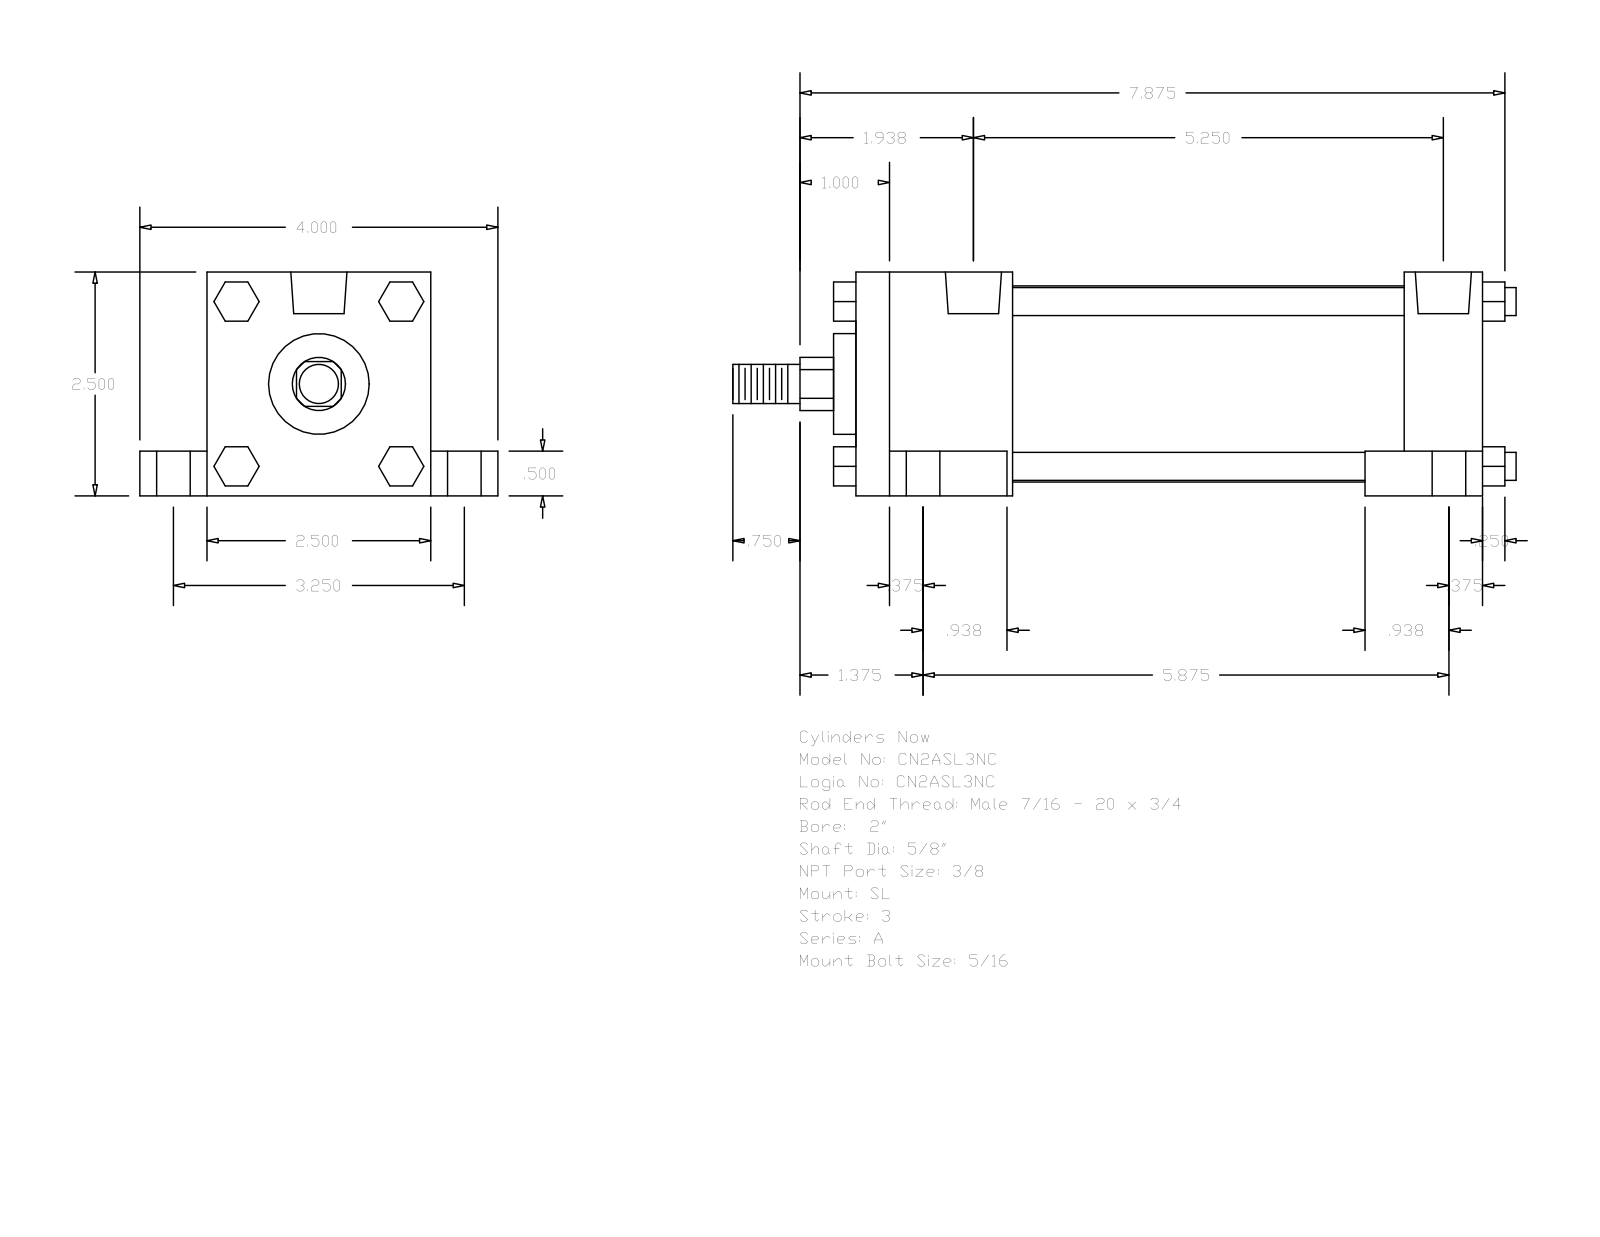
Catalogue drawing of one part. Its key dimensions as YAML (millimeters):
part_name: "A_SL__0200_0.625"
step_written_by: "GSSL Pune (CONFIG_CONTROL_DESIGN)"
units: millimeters
bodies: {solids: 0, faces: 148, planar: 112, cylindrical: 36, other: 0}
overall_size: [222.25, 101.6, 63.5]
round_holes:
  - {diameter: 5.56, count: 4}
  - {diameter: 9.53, count: 4}
  - {diameter: 15.88, count: 4}
  - {diameter: 15.93, count: 2}
round_bosses_or_shafts:
  - {diameter: 7.94, count: 4}
  - {diameter: 55.63, count: 1}
  - {diameter: 28.57, count: 1}
  - {diameter: 15.88, count: 1}
  - {diameter: 11.11, count: 1}
partial_cylinders:
  - {radius: 7.54, count: 1}
face_to_face_distances: [63.5, 177.8, 50.8, 12.7, 19.05, 82.55, 44.45, 133.35, 155.57, 111.12]
hole_center_spacings: [41.3, 41.64, 43.67, 45.13, 82.54, 125.4, 137.31, 141.11]
